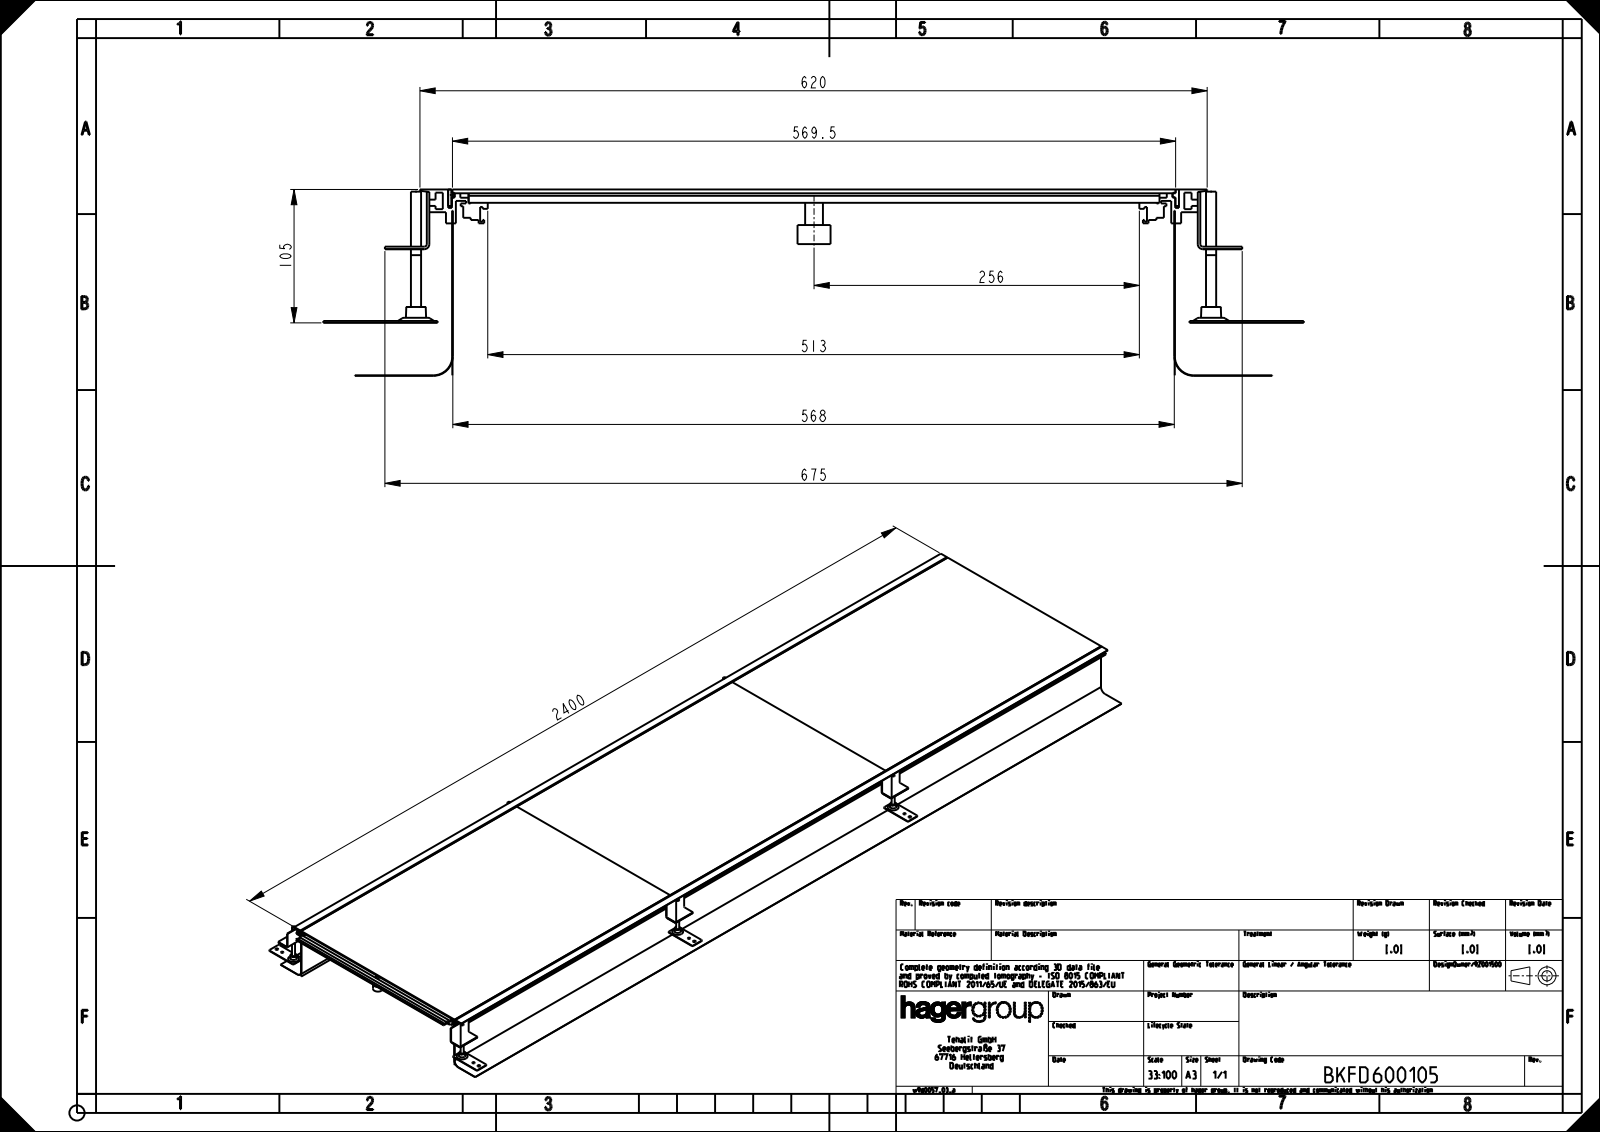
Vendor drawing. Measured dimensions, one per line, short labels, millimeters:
name: U05644KUN; U05650KUN; U05647KUN; U05826KUN (+8 more)
written by: CREO PARAMETRIC BY PTC INC, 2020281 (AUTOMOTIVE_DESIGN)
unit: mm
bodies: 62 solids, 1026 faces (600 planar, 354 cylindrical, 72 other)
size: 2432.5 × 772.13 × 146.7
volume: 9 044 000 mm³; area: 7 199 000 mm²
holes: 15× ⌀7, 9× ⌀8, 9× ⌀10, 6× ⌀6, 6× ⌀8.5, 6× ⌀11.5, 6× ⌀17.5, 6× ⌀23
bosses: 9× ⌀26, 9× ⌀14, 9× ⌀11.9, 6× ⌀20, 6× ⌀8
rounds: 92× R2, 24× R3, 20× R0.5, 2× R4, 2× R15, 2× R15.4
face distances: 3, 0.4, 568.55, 143.7, 146.7, 143.3, 146.3, 7.5, 6.5, 568.95
hole spacings: 800, 1600, 800.25, 801.1, 802.4, 1042.3, 1055.24, 1083.09
